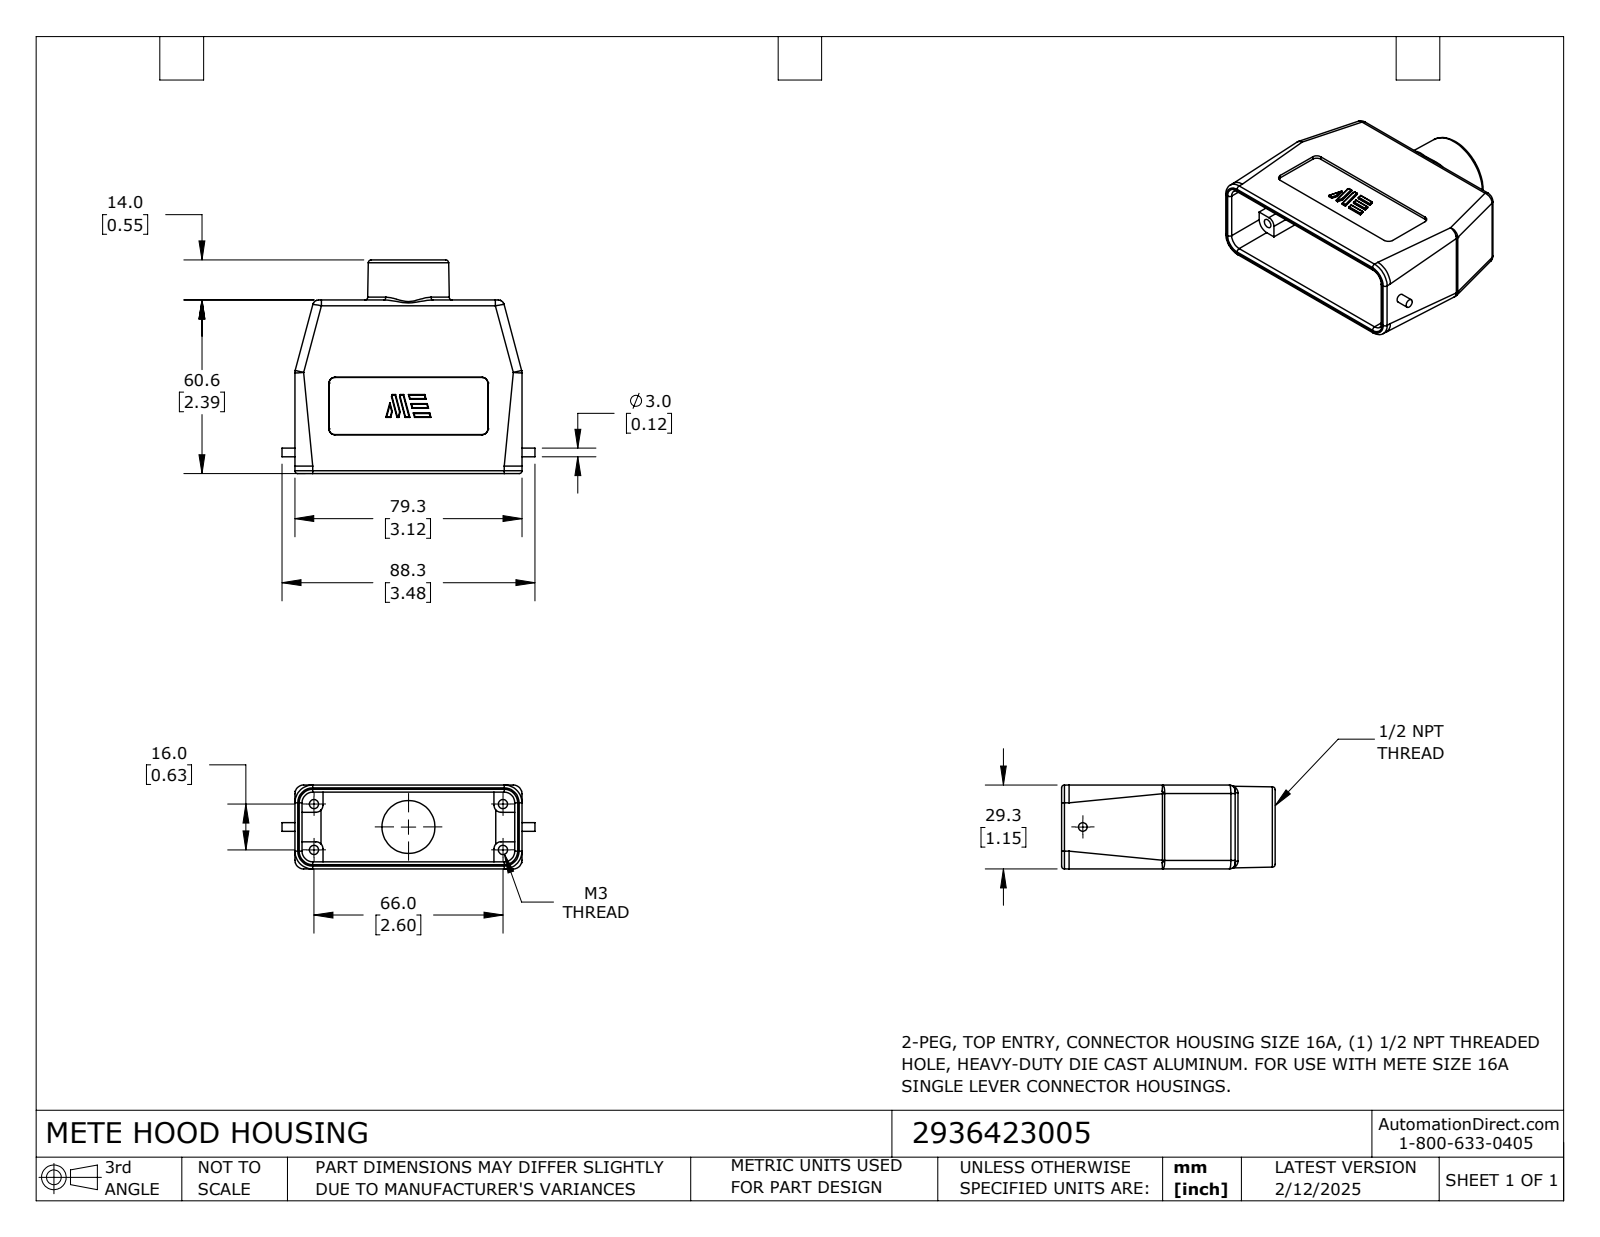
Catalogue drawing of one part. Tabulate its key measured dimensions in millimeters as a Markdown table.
| quantity | value |
| --- | --- |
| part name | 2936423005 |
| STEP written by | SolidWorks 2024 (CONFIG_CONTROL_DESIGN) |
| units | millimeters |
| bodies | 1 solid, 253 faces (112 planar, 96 cylindrical, 45 other) |
| overall size | 88.3 × 74.6 × 29.3 |
| volume | 41 210 mm³ |
| surface area | 29 730 mm² |
| round holes (diameter × count) | 3.2 × 4, 18.5 × 1, 21 × 1 |
| round bosses / shafts (diameter × count) | 3 × 1 |
| partial cylindrical surfaces (radius × count) | 0.2 × 38, 1 × 8, 2 × 4, 2.5 × 4, 3 × 4, 6.2 × 4, 2.9 × 2 |
| main face-to-face distances | 2.5, 26.8, 24.3, 29.3, 28.3, 1, 1.5, 25.8, 27.3, 76.8 |
| hole center spacings | 34, 16, 66, 67.9 |
